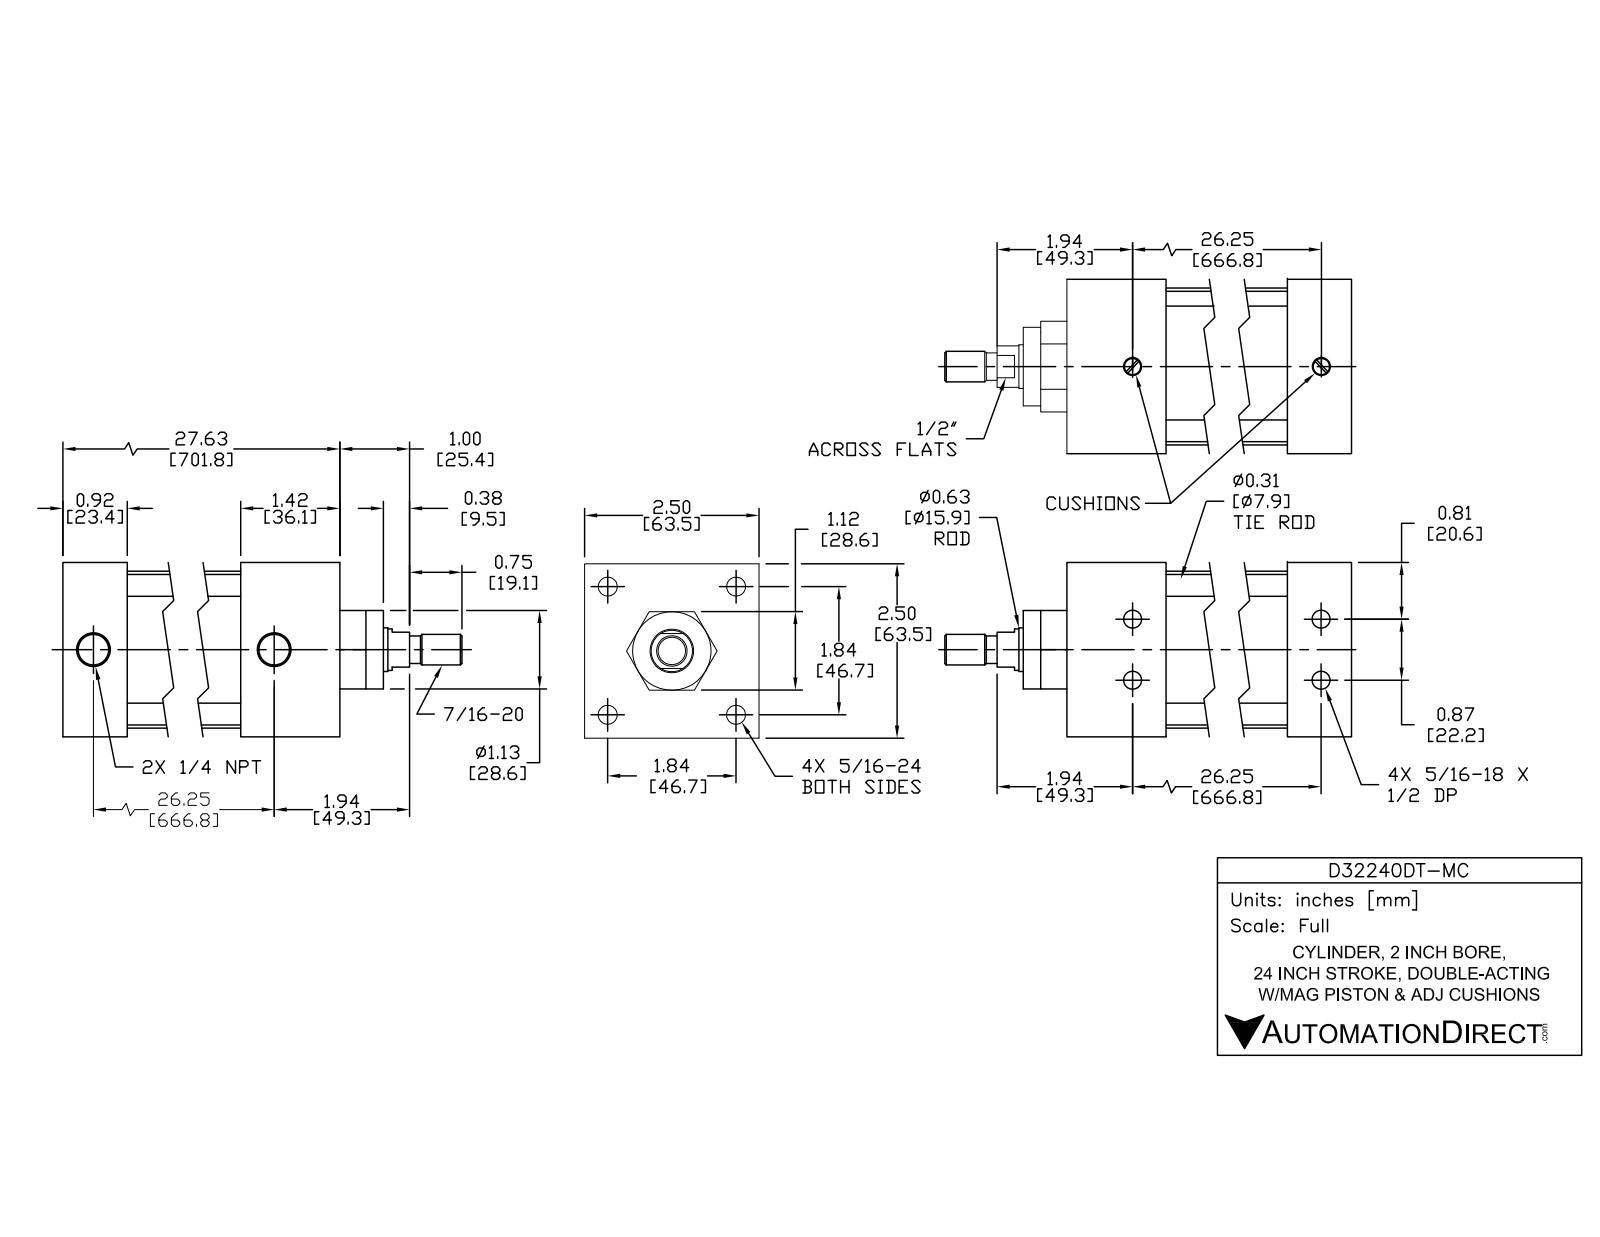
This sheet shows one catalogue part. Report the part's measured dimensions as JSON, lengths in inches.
{"part_name": "D32240DT-MC; D32240DT-M BODY; D32240DT-M PISTON", "step_written_by": "SolidWorks 2015 (AUTOMOTIVE_DESIGN)", "units": "inches", "bodies": {"solids": 12, "faces": 298, "planar": 94, "cylindrical": 114, "other": 90}, "overall_size": [29.371, 2.5, 2.5], "volume_in3": 53.15, "surface_area_in2": 575.9, "round_holes": [[0.252, 4], [0.267, 4], [0.359, 4], [0.5, 4], [0.297, 2], [0.477, 2], [0.625, 1], [0.628, 1], [2, 1]], "round_bosses_or_shafts": [[0.484, 4], [0.313, 4], [0.282, 4], [2.25, 1], [1.997, 1], [1.12, 1], [0.622, 1], [0.59, 1]], "partial_cylinders_radius": [[0.25, 4]], "face_to_face_distances": [2.5, 0.08, 25.201, 27.621, 1.42, 26.201, 26.701, 25.281, 0.92, 1], "hole_center_spacings": [0.437, 1.307, 1.848, 26.249, 26.245, 0.875, 2.613, 26.26]}
